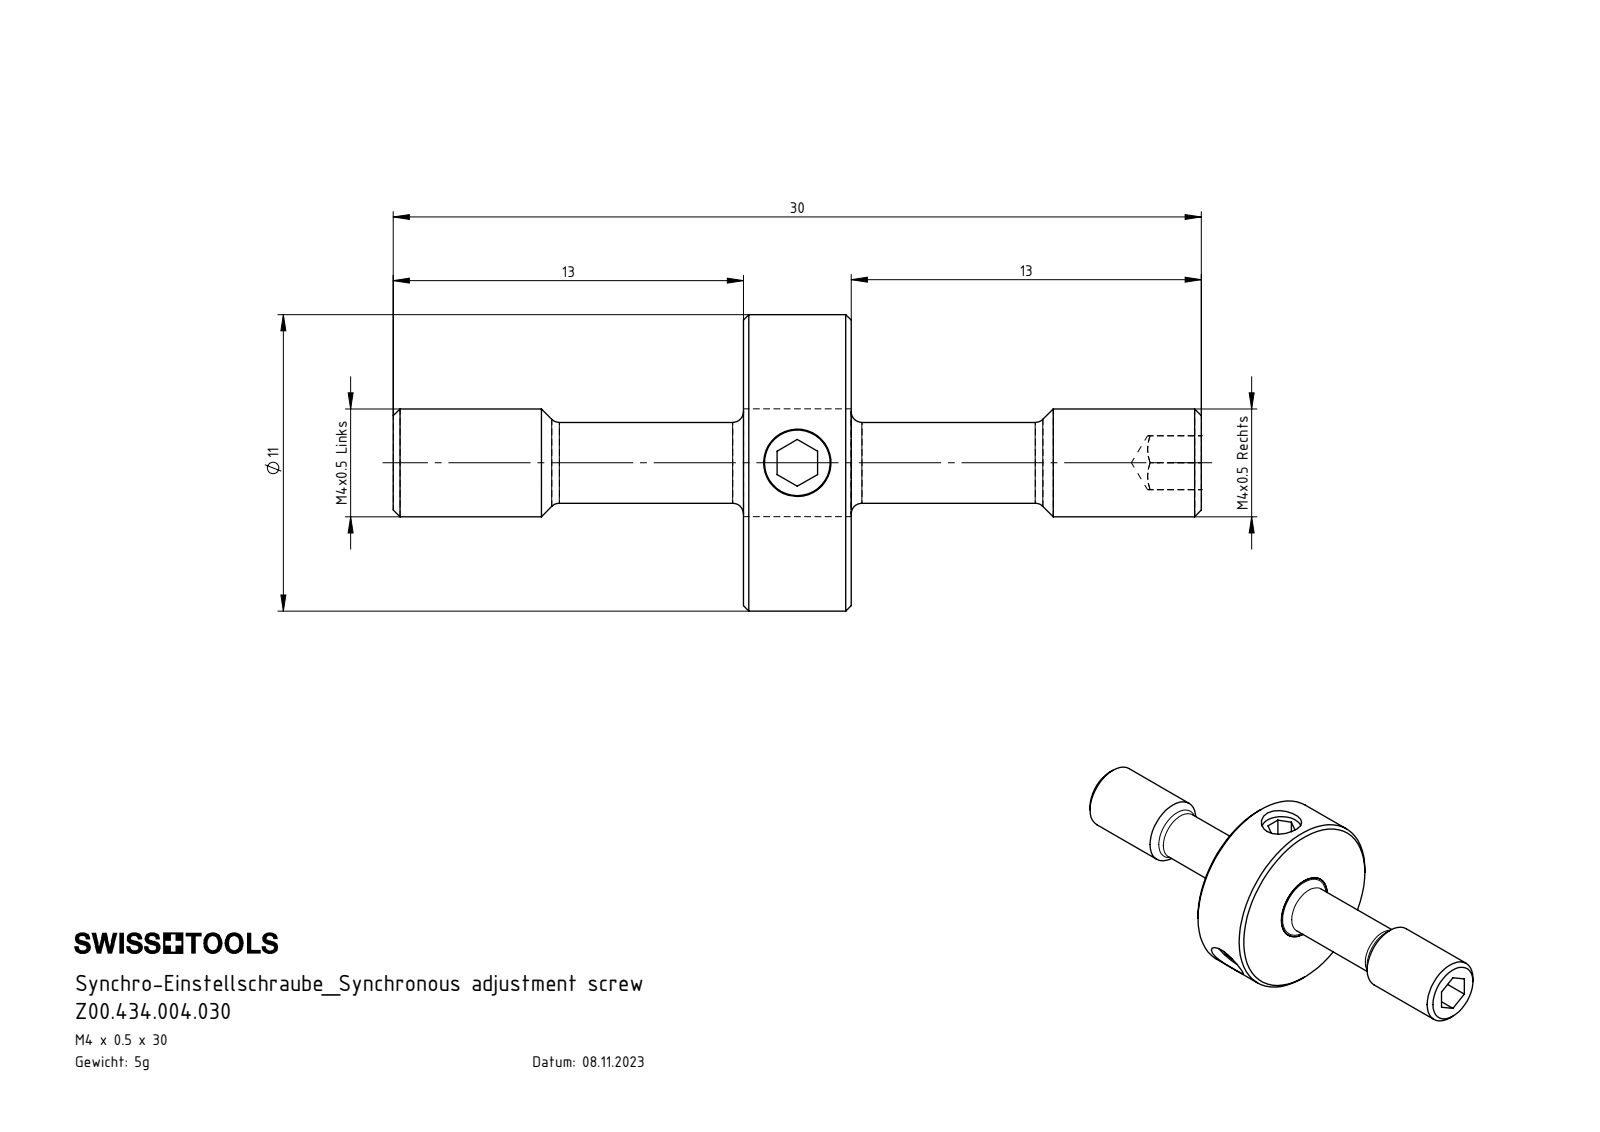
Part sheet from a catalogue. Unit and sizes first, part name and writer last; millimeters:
Units: millimetres
Overall size (bounding box): 30 × 11 × 11
Round holes (diameter × count): ⌀2.5 ×3
Round bosses / shafts (diameter × count): ⌀3 ×4, ⌀11 ×1, ⌀4 ×1
Main face-to-face distances: 4, 13, 17, 1.5, 2, 14.25, 15.75, 1.25, 2.75, 3
Volume: 614 mm³ · Surface area: 925 mm²
Bodies: 5 solids, 99 faces (39 planar, 26 cylindrical, 34 other)
Part name (STEP PRODUCT): ISO 4026 - M3 x 3; Z00.434.004.030; Z25-ER3.002.004_A; Z32-ER3.001.030_A
STEP written by: SolidWorks 2022 (AUTOMOTIVE_DESIGN)
